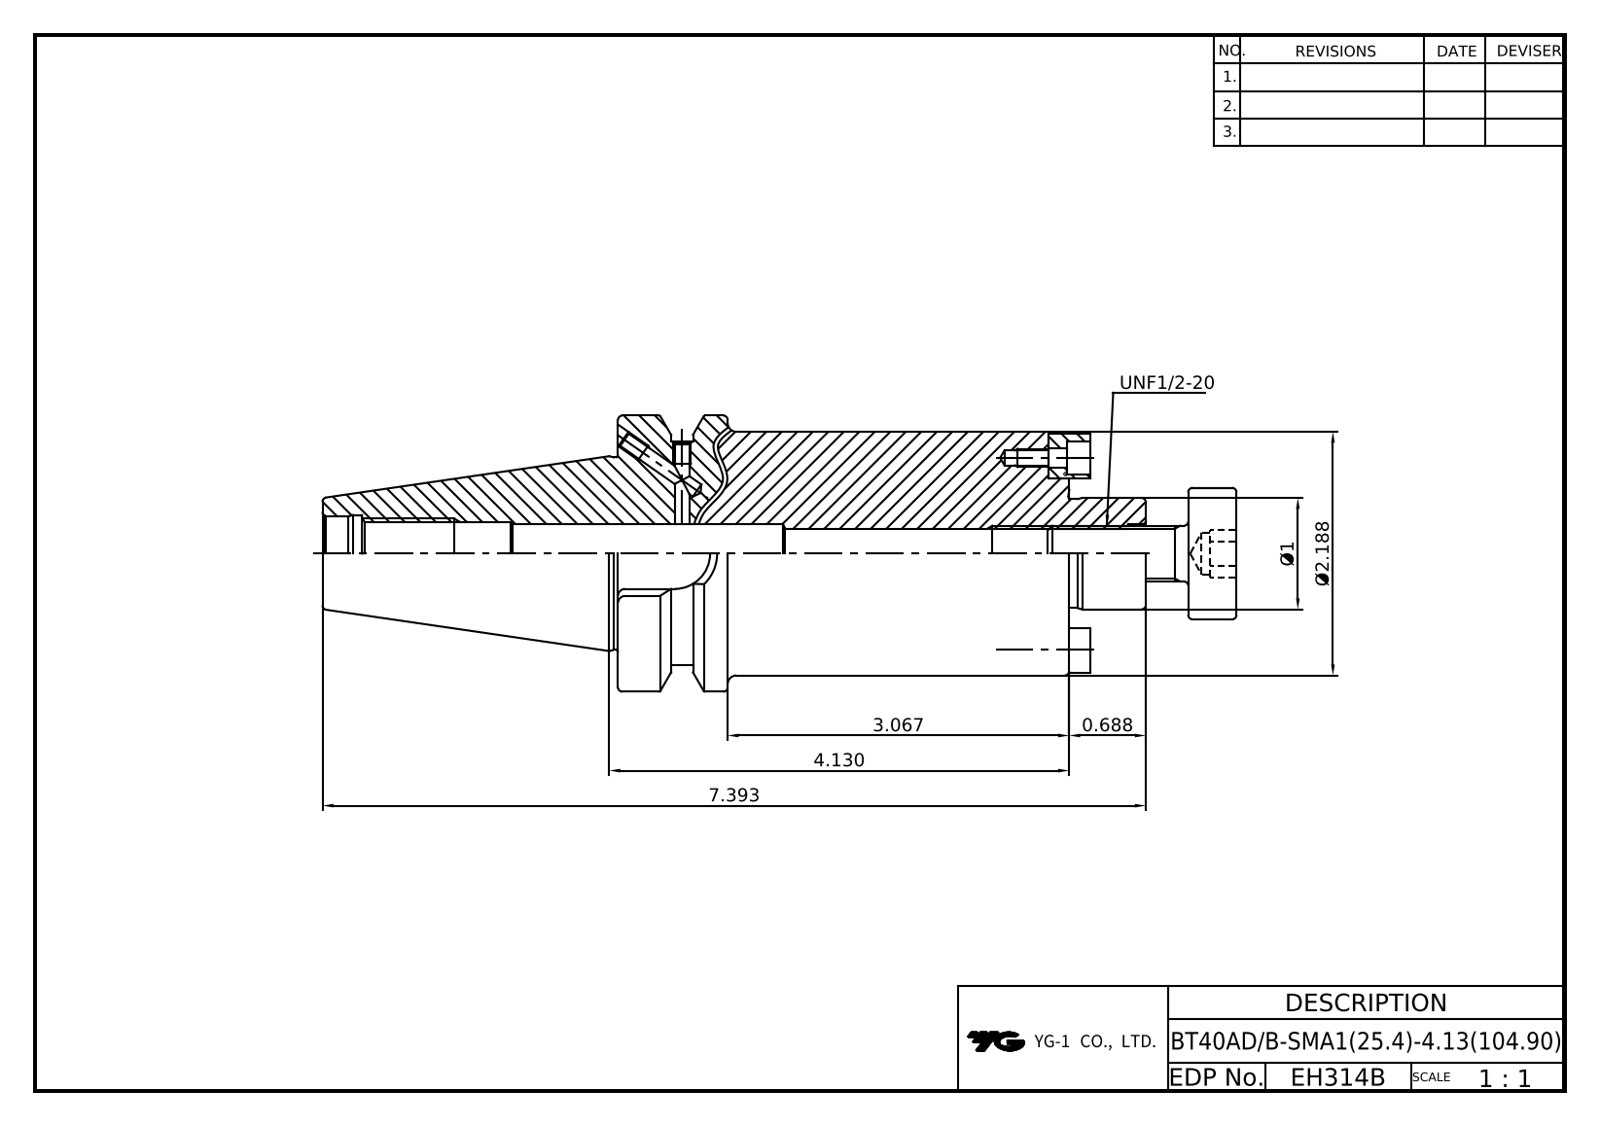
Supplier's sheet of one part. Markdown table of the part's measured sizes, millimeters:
| quantity | value |
| --- | --- |
| part name | LO-BT40ADB-SMA25.4-104.9; DRIVE KEY-9.52x9.52x10.2; HEX'' WRENCH BOLT-UNC#8-32x3_8L; COLLAR BOLT-UNF1_2-20x32L |
| STEP written by | Autodesk Inventor 2026 (AUTOMOTIVE_DESIGN) |
| units | millimeters |
| bodies | 6 solids, 147 faces (72 planar, 44 cylindrical, 31 other) |
| overall size | 208.8 × 63 × 63 |
| volume | 317 900 mm³ |
| surface area | 47 950 mm² |
| round holes (diameter × count) | 3.3 × 4, 4 × 4, 3.3 × 2, 4.5 × 2, 7.5 × 2, 9.5 × 1, 11.3 × 1, 13.5 × 1, 13.8 × 1, 17 × 1, 17.6 × 1 |
| round bosses / shafts (diameter × count) | 6.9 × 2, 4.2 × 2, 63 × 1, 55.6 × 1, 52.6 × 1, 44 × 1, 30 × 1, 25.4 × 1 |
| partial cylindrical surfaces (radius × count) | 4.7 × 2, 8.1 × 1 |
| main face-to-face distances | 102.9, 25, 116.4, 141.4, 38.5, 77.9, 130.4, 105.4, 27.5, 11 |
| hole center spacings | 21.8, 43.7 |
